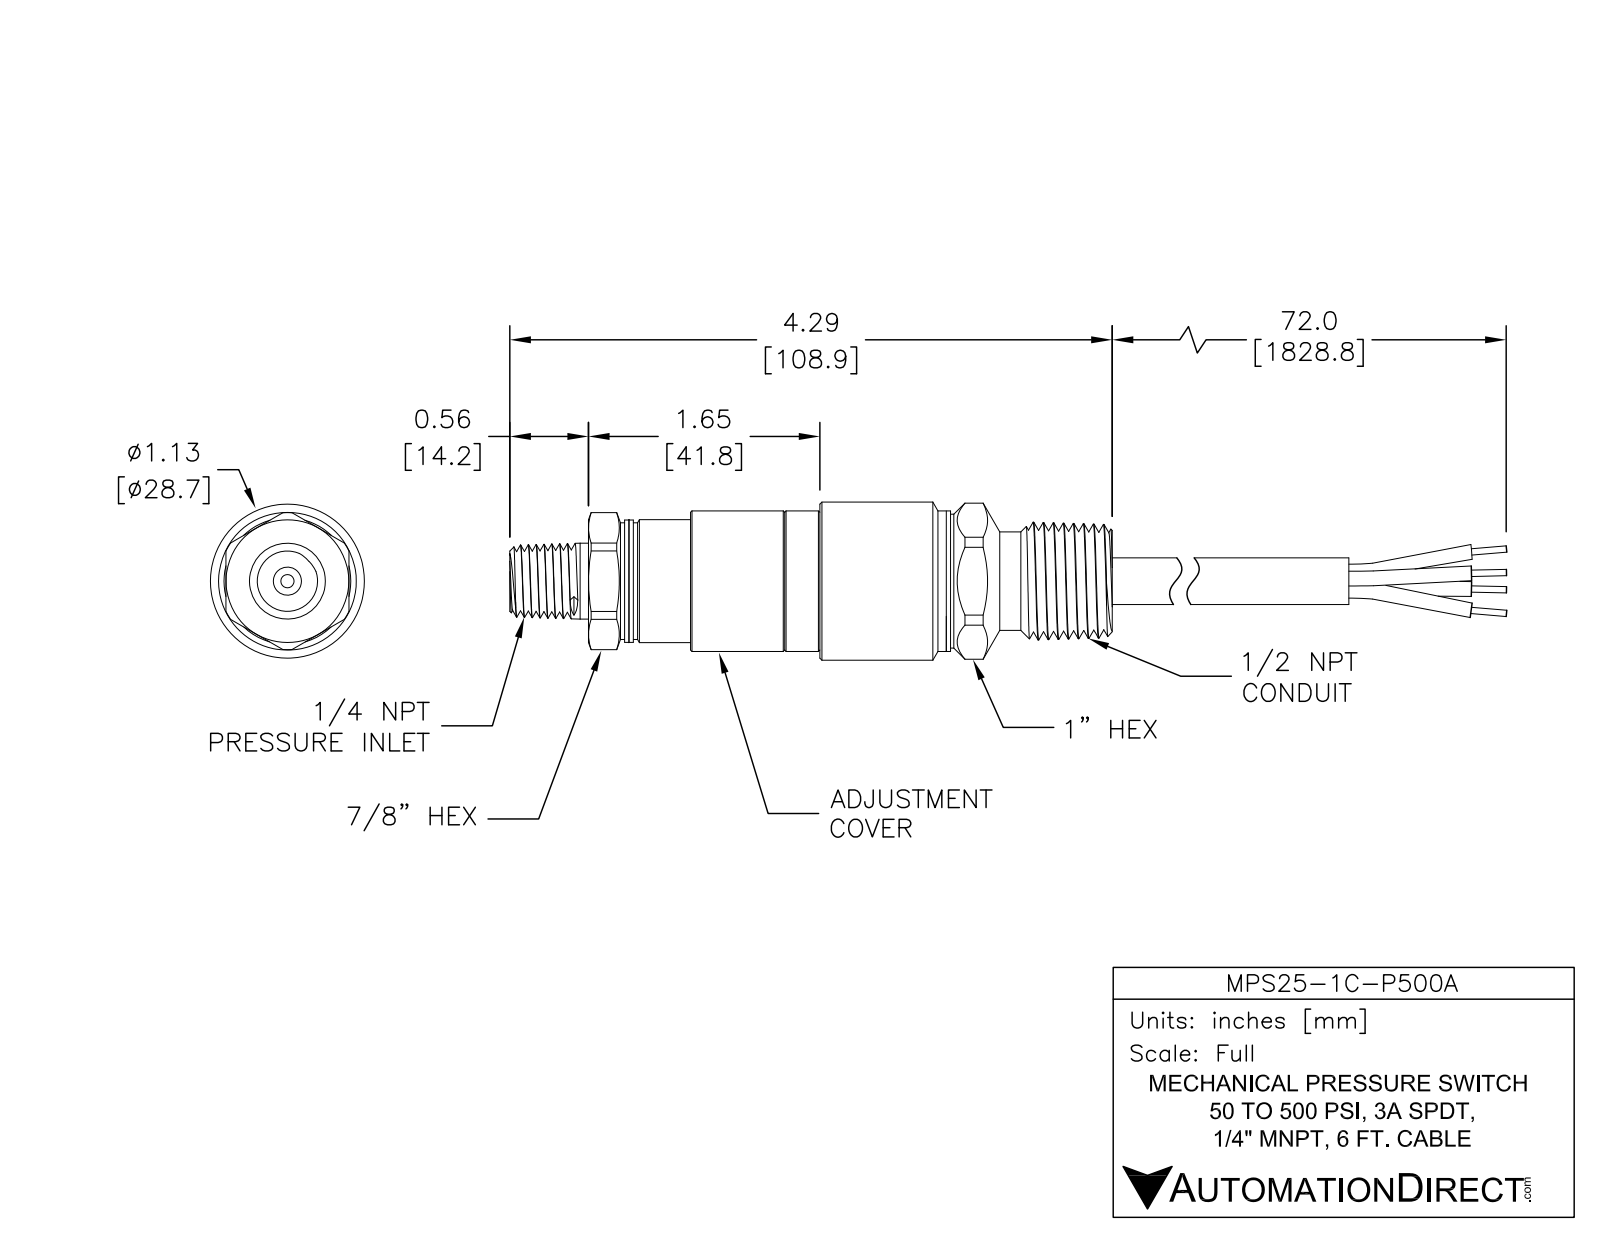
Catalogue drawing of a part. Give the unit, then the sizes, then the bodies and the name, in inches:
Units: inches
Overall size (bounding box): 8.913 × 1.125 × 1.125
Round holes (diameter × count): ⌀0.045 ×4, ⌀0.105 ×4, ⌀0.04 ×3, ⌀0.058 ×3, ⌀0.094 ×1, ⌀0.096 ×1, ⌀0.111 ×1, ⌀0.125 ×1, ⌀0.222 ×1, ⌀0.332 ×1, ⌀0.34 ×1, ⌀0.43 ×1
Round bosses / shafts (diameter × count): ⌀0.045 ×4, ⌀0.105 ×3, ⌀0.045 ×3, ⌀0.105 ×2, ⌀0.062 ×2, ⌀1.125 ×1, ⌀1 ×1, ⌀0.952 ×1
Partial cylindrical surfaces — rounded edges, fillets, slot ends (radius × count): R0.052 ×4, R0.053 ×3, R0.08 ×2, R0.11 ×1, R0.292 ×1, R0.432 ×1, R0.487 ×1, R0.505 ×1
Main face-to-face distances: 0.063, 0.937, 1, 1.97, 1.359, 0.612, 1.357, 1.969, 0.287, 0.289
Hole centre spacings: 0.301, 0.425, 0.187, 0.223, 0.243, 0.244, 0.372, 0.373
Volume: 1.869 in³ · Surface area: 48.83 in²
Bodies: 12 solids, 570 faces (96 planar, 225 cylindrical, 249 other)
Part name (STEP PRODUCT): MPS25-1C-DV15A
STEP written by: SolidWorks 2017 (AUTOMOTIVE_DESIGN)
